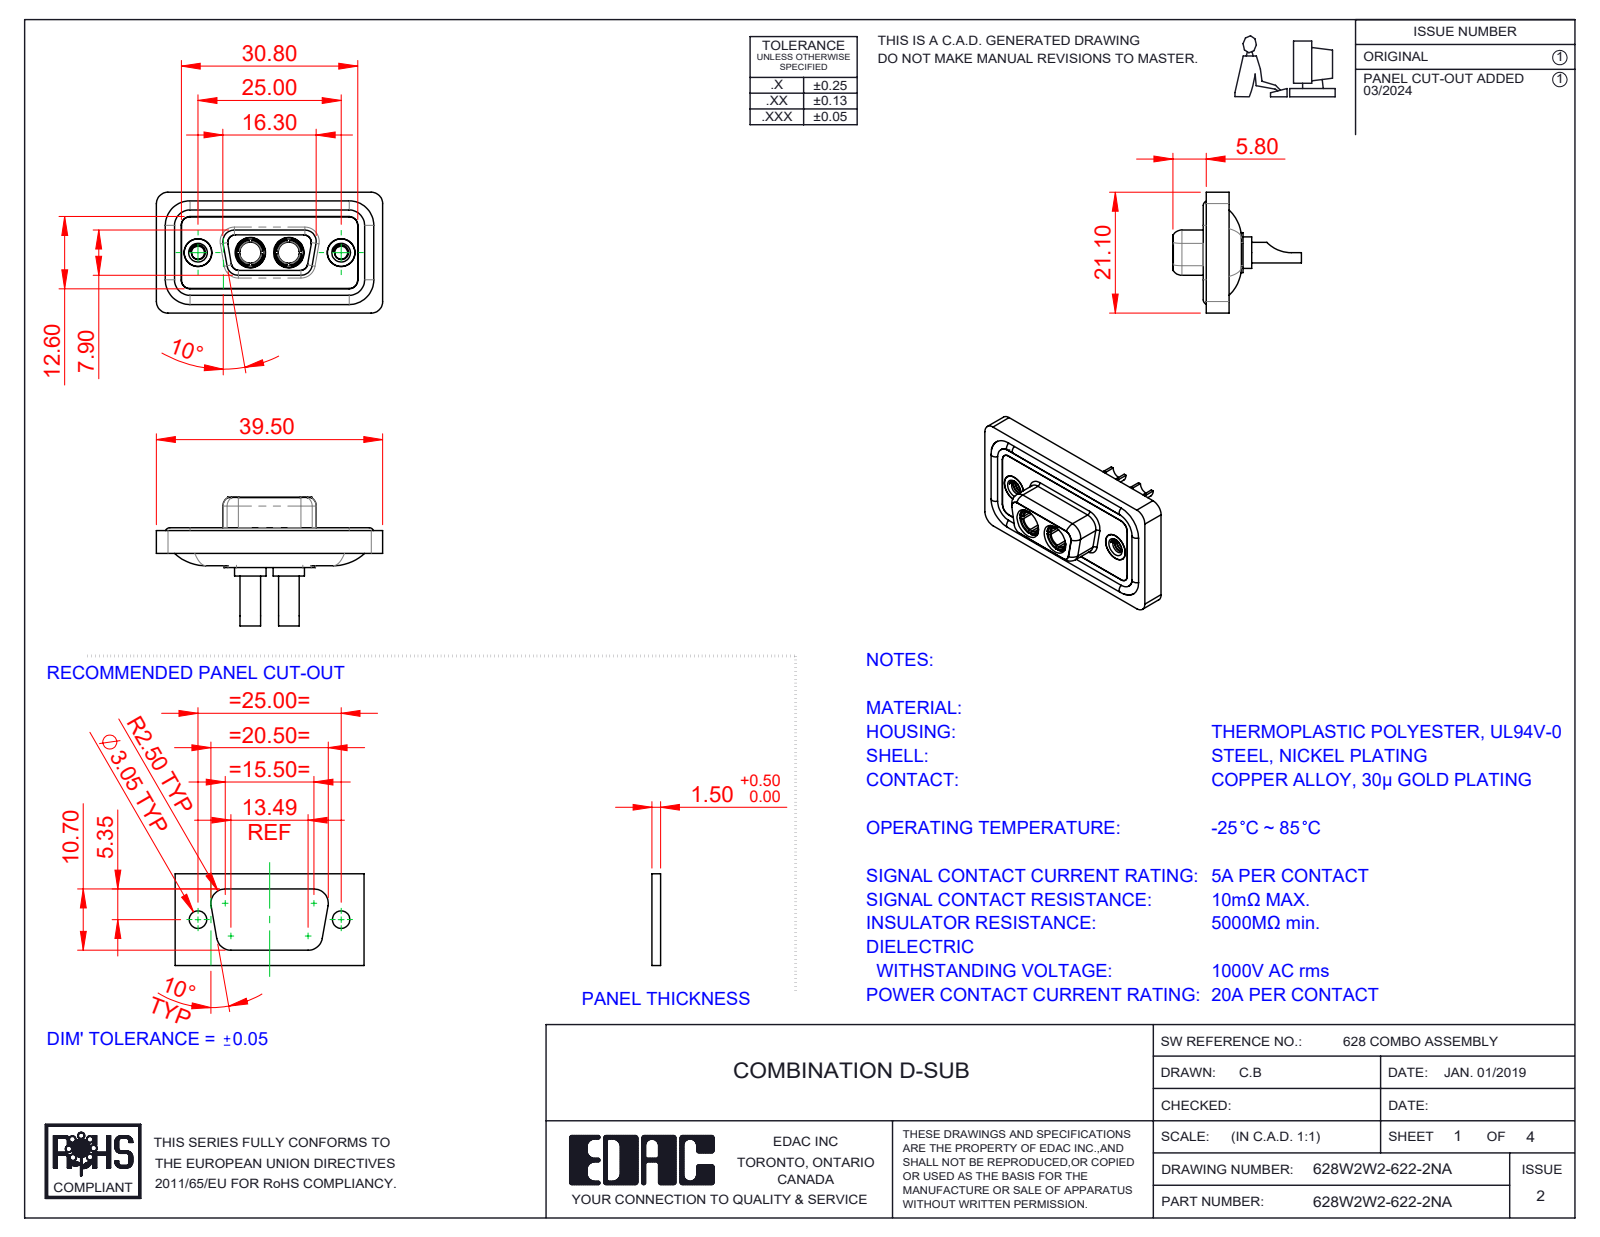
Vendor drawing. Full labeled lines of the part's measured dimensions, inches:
Part name (STEP PRODUCT): 628Combo Threaded Rivet_A; 628Combo Shell Front_09 Contacts; 628W2W2-622-2NA; 628Combo Shell Rear_09 Contacts (+3 more)
STEP written by: SolidWorks 2023 (CONFIG_CONTROL_DESIGN)
Units: inches
Bodies: 11 solids, 544 faces (169 planar, 242 cylindrical, 133 other)
Overall size (bounding box): 1.555 × 0.884 × 0.831
Volume: 0.289 in³ · Surface area: 12.09 in²
Round holes (diameter × count): ⌀0.191 ×4, ⌀0.089 ×2, ⌀0.106 ×2, ⌀0.146 ×2, ⌀0.157 ×2, ⌀0.159 ×2, ⌀0.197 ×2, ⌀0.209 ×2
Round bosses / shafts (diameter × count): ⌀0.063 ×4, ⌀0.217 ×2, ⌀0.205 ×2, ⌀0.195 ×2, ⌀0.195 ×2, ⌀0.189 ×2, ⌀0.187 ×2, ⌀0.148 ×2
Partial cylindrical surfaces — rounded edges, fillets, slot ends (radius × count): R0.059 ×22, R0.079 ×18, R0.053 ×8, R0.063 ×8, R0.01 ×4, R0.02 ×4, R0.024 ×4, R0.026 ×4
Main face-to-face distances: 0.016, 0.071, 0.043, 0.114, 0.02, 0.063, 0.222, 0.293, 0.211, 0.059
Hole centre spacings: 0.36, 0.624, 0.265, 0.984
